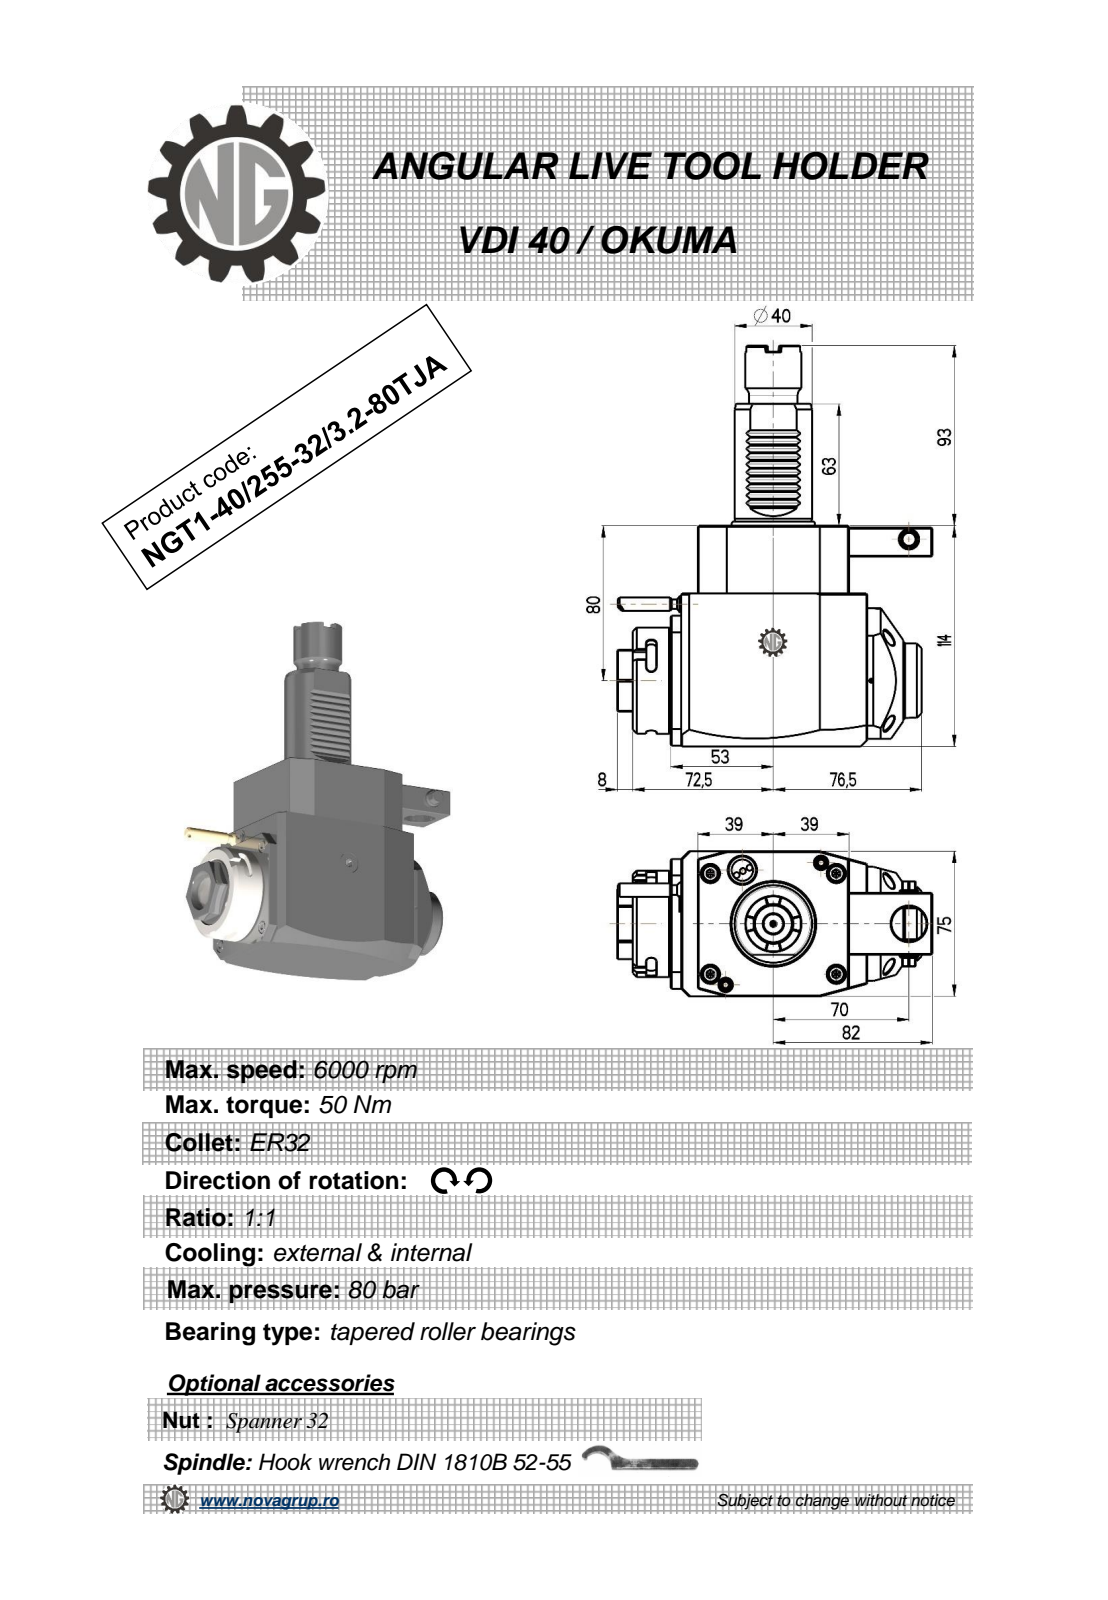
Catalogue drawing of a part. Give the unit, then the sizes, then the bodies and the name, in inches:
Units: inches
Overall size (bounding box): 8.15 × 6.398 × 2.953
Round holes (diameter × count): ⌀0.098 ×1, ⌀0.118 ×1, ⌀0.374 ×1, ⌀0.709 ×1, ⌀0.906 ×1
Round bosses / shafts (diameter × count): ⌀0.353 ×2, ⌀2.165 ×1, ⌀1.89 ×1, ⌀1.575 ×1, ⌀1.516 ×1, ⌀1.142 ×1, ⌀0.984 ×1, ⌀0.394 ×1
Partial cylindrical surfaces — rounded edges, fillets, slot ends (radius × count): R0.012 ×10, R0.098 ×6, R7.087 ×2, R0.02 ×1, R0.152 ×1, R0.167 ×1, R0.394 ×1, R0.965 ×1
Main face-to-face distances: 2.953, 4.488, 0.551, 1.319, 3.11, 3.622, 3.071, 0.846, 0.768, 4.39
Hole centre spacings: 1.47, 1.701, 2.854
Volume: 60.87 in³ · Surface area: 119.2 in²
Bodies: 1 solid, 390 faces (202 planar, 80 cylindrical, 108 other)
Part name (STEP PRODUCT): NGT1_40_255_32_3_2_80TJA
STEP written by: PRO/ENGINEER BY PARAMETRIC TECHNOLOGY CORPORATION, 2010280 (CONFIG_CONTROL_DESIGN)
